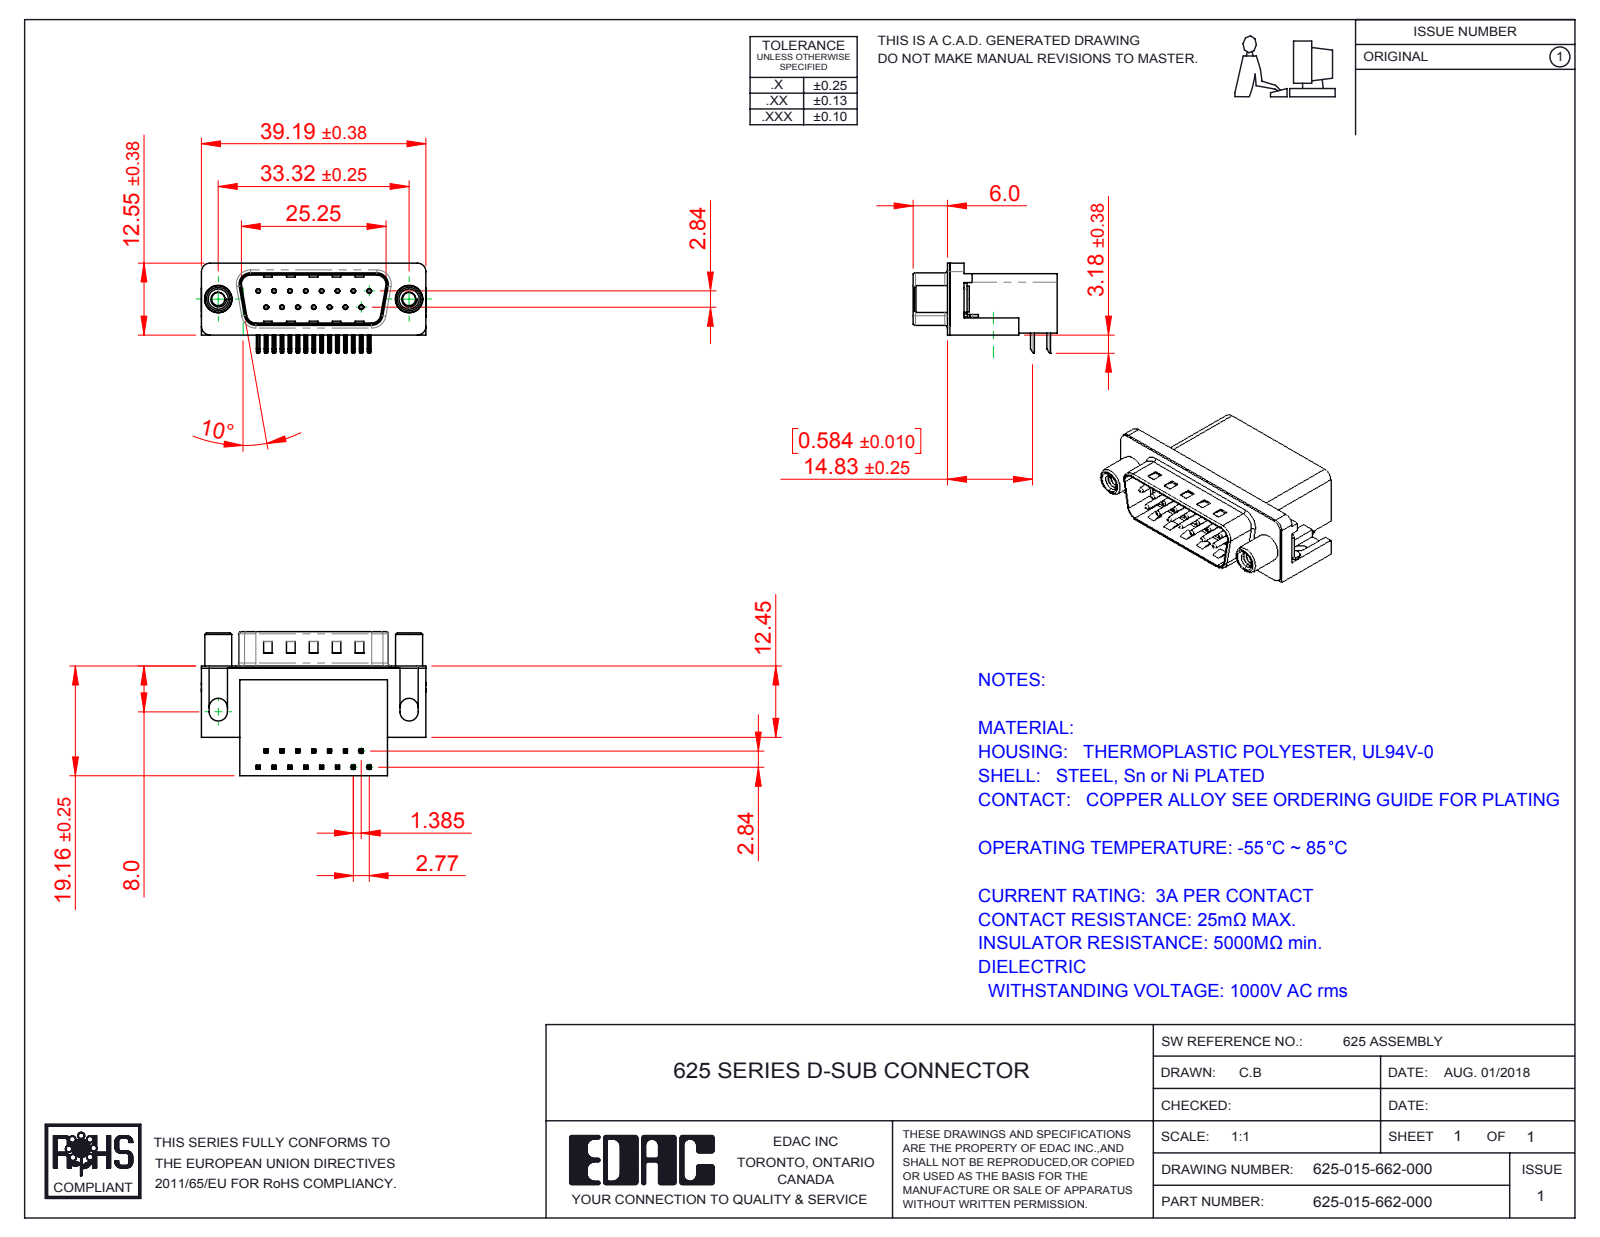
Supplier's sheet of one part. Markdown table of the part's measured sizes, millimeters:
| quantity | value |
| --- | --- |
| part name | 625 Non Board Mount; 625 Shell_15 Socket; 625 Round Threaded Standoff; 625 Contact Bottom (+3 more) |
| STEP written by | SolidWorks 2016 (CONFIG_CONTROL_DESIGN) |
| units | millimeters |
| bodies | 21 solids, 1471 faces (887 planar, 451 cylindrical, 133 other) |
| overall size | 39.22 × 25.16 × 15.73 |
| volume | 6 306 mm³ |
| surface area | 6 490 mm² |
| round holes (diameter × count) | 0.35 × 15, 0.8 × 15, 2.3 × 2, 3.1 × 2, 4 × 2, 4.8 × 2, 5 × 2 |
| round bosses / shafts (diameter × count) | 0.75 × 15, 4.9 × 2, 4.7 × 2, 4.5 × 2, 3.85 × 2 |
| partial cylindrical surfaces (radius × count) | 0.25 × 60, 0.12 × 30, 1 × 16, 0.5 × 9, 1.6 × 8, 1.5 × 6, 0.9 × 4, 2 × 4 |
| main face-to-face distances | 0.4, 10.35, 18.76, 2.1, 10.46, 1.7, 10.86, 19.16, 8.76, 16.26 |
| hole center spacings | 3.16, 2.77, 5.54, 8.31, 11.08, 5.03, 5.04, 7.48 |
